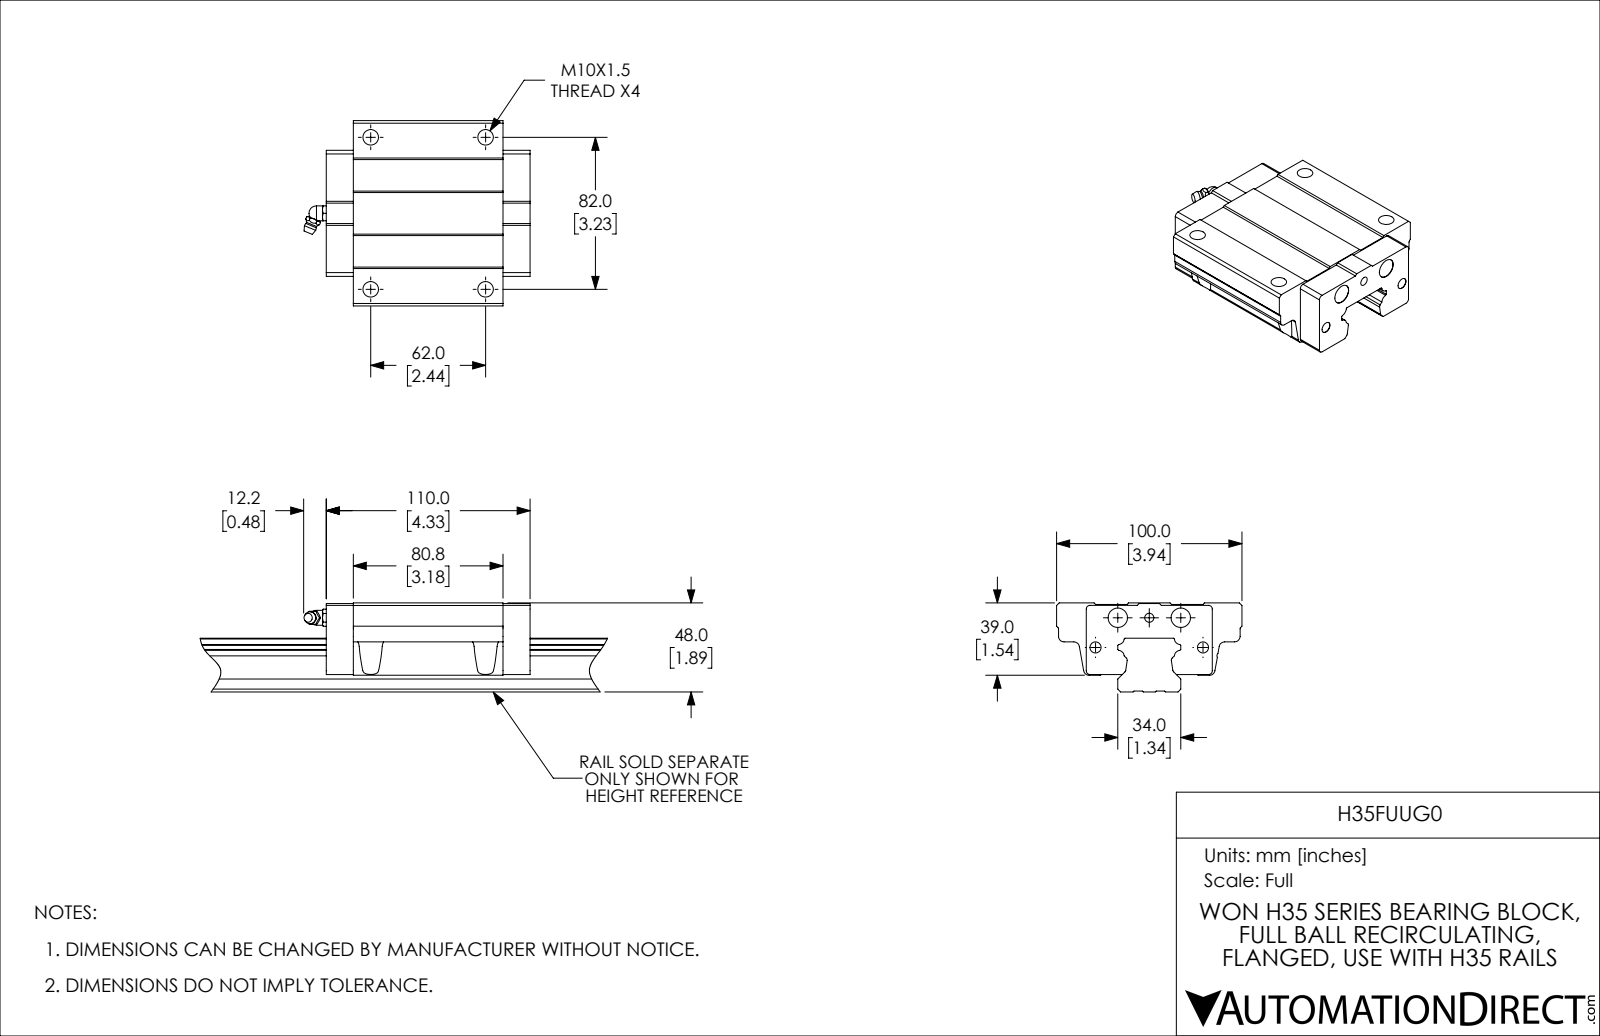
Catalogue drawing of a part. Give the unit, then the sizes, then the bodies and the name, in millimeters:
Units: millimetres
Overall size (bounding box): 122 × 100 × 39
Round holes (diameter × count): ⌀8.38 ×4, ⌀6 ×2, ⌀10.5 ×2, ⌀4.92 ×1
Round bosses / shafts (diameter × count): ⌀8 ×1, ⌀6 ×1
Partial cylindrical surfaces — rounded edges, fillets, slot ends (radius × count): R3 ×6, R1.5 ×5, R2 ×4, R3.2 ×4, R7 ×4, R0.5 ×2, R1 ×2
Main face-to-face distances: 19, 19.6, 38.6, 37.8, 18.2, 0.8, 0.5, 16, 84, 110
Hole centre spacings: 17, 20, 33.12, 48.7, 62, 82, 102.8, 34
Volume: 279 379 mm³ · Surface area: 41 082 mm²
Bodies: 2 solids, 184 faces (93 planar, 69 cylindrical, 22 other)
Part name (STEP PRODUCT): H35FUUG0
STEP written by: SolidWorks 2019 (CONFIG_CONTROL_DESIGN)
